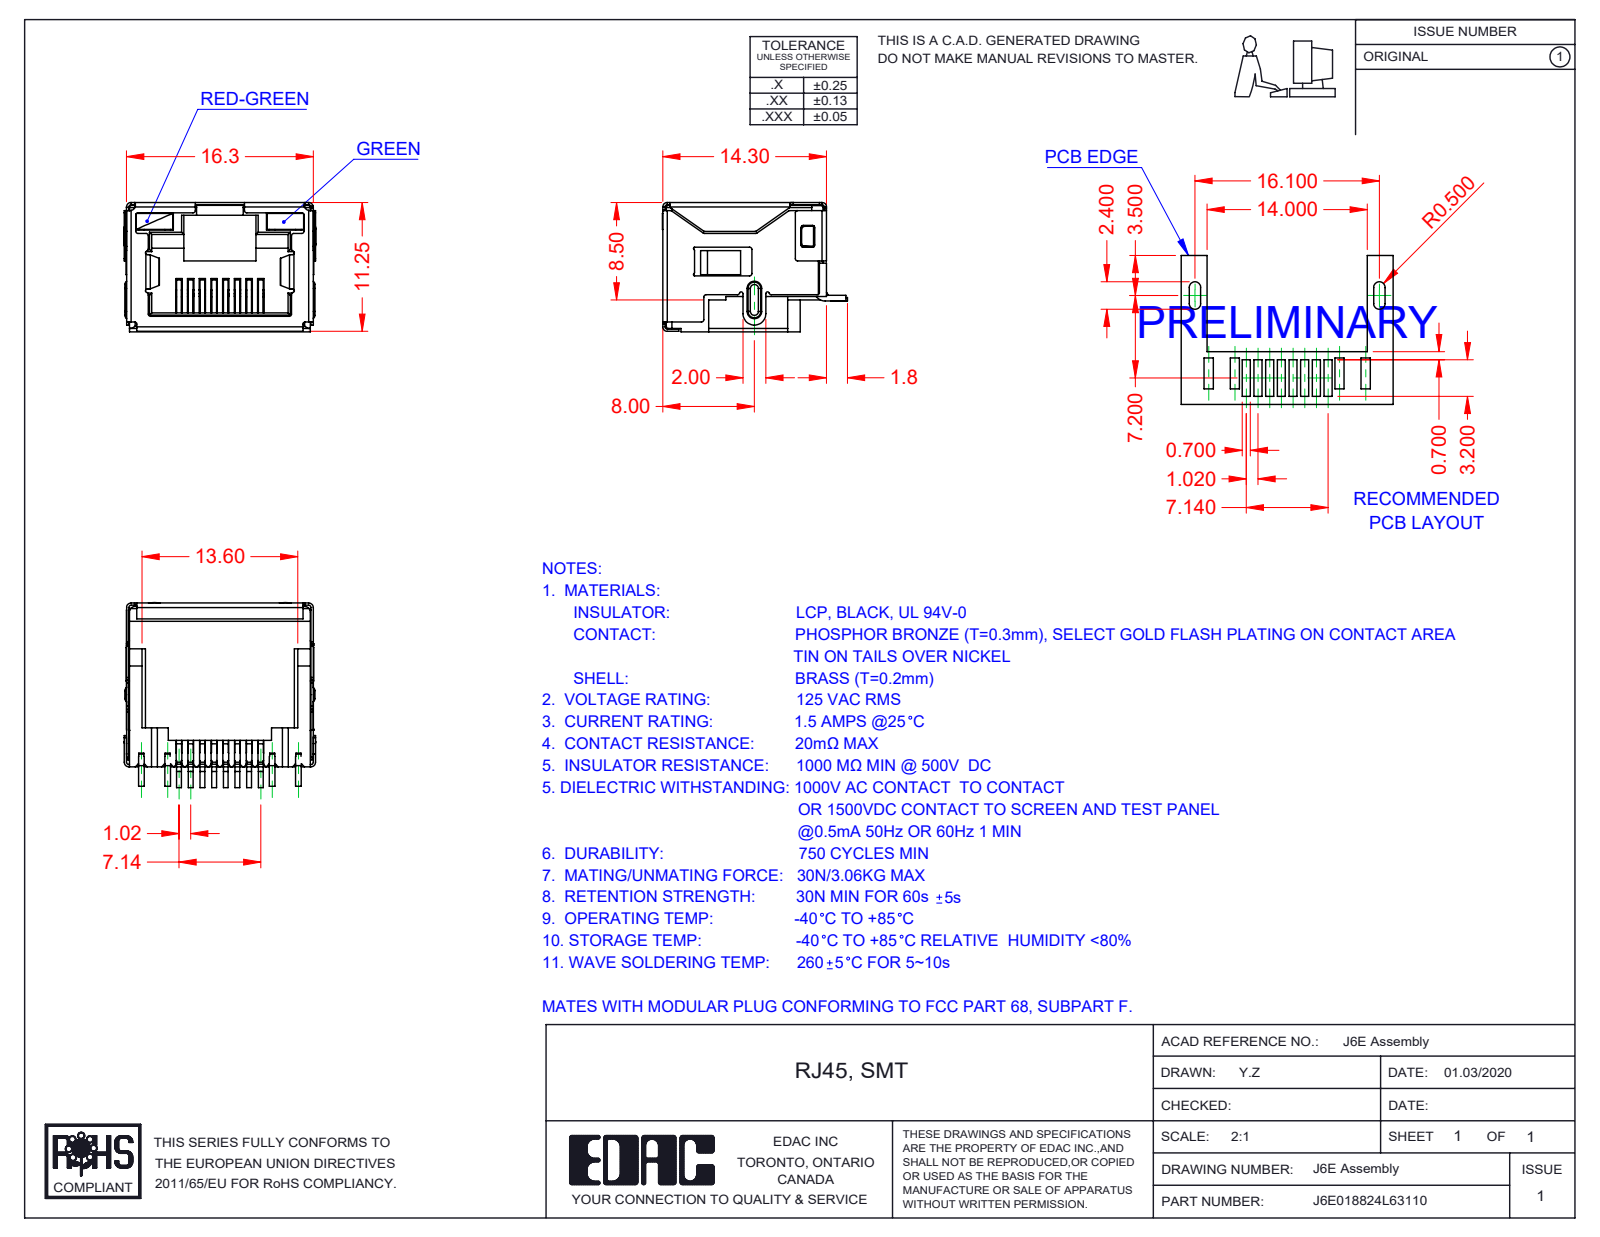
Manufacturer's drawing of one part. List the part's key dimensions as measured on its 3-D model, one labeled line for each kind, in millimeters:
Part name (STEP PRODUCT): 6E Insulator_LED; 6E Contacts; J6E018824L63110; 6E Shield_LED (+2 more)
STEP written by: SolidWorks 2016 (CONFIG_CONTROL_DESIGN)
Units: millimetres
Bodies: 12 solids, 1498 faces (1099 planar, 349 cylindrical, 50 other)
Overall size (bounding box): 16.75 × 16.15 × 11.3
Volume: 1 109 mm³ · Surface area: 4 045 mm²
Partial cylindrical surfaces — rounded edges, fillets, slot ends (radius × count): R0.2 ×82, R0.25 ×17, R0.4 ×13, R0.5 ×13, R0.1 ×10, R0.15 ×7, R0.3 ×4, R1 ×3
Main face-to-face distances: 11.05, 16.05, 16.1, 15.85, 11.1, 11.3, 2.4, 0.7, 9.85, 0.49
